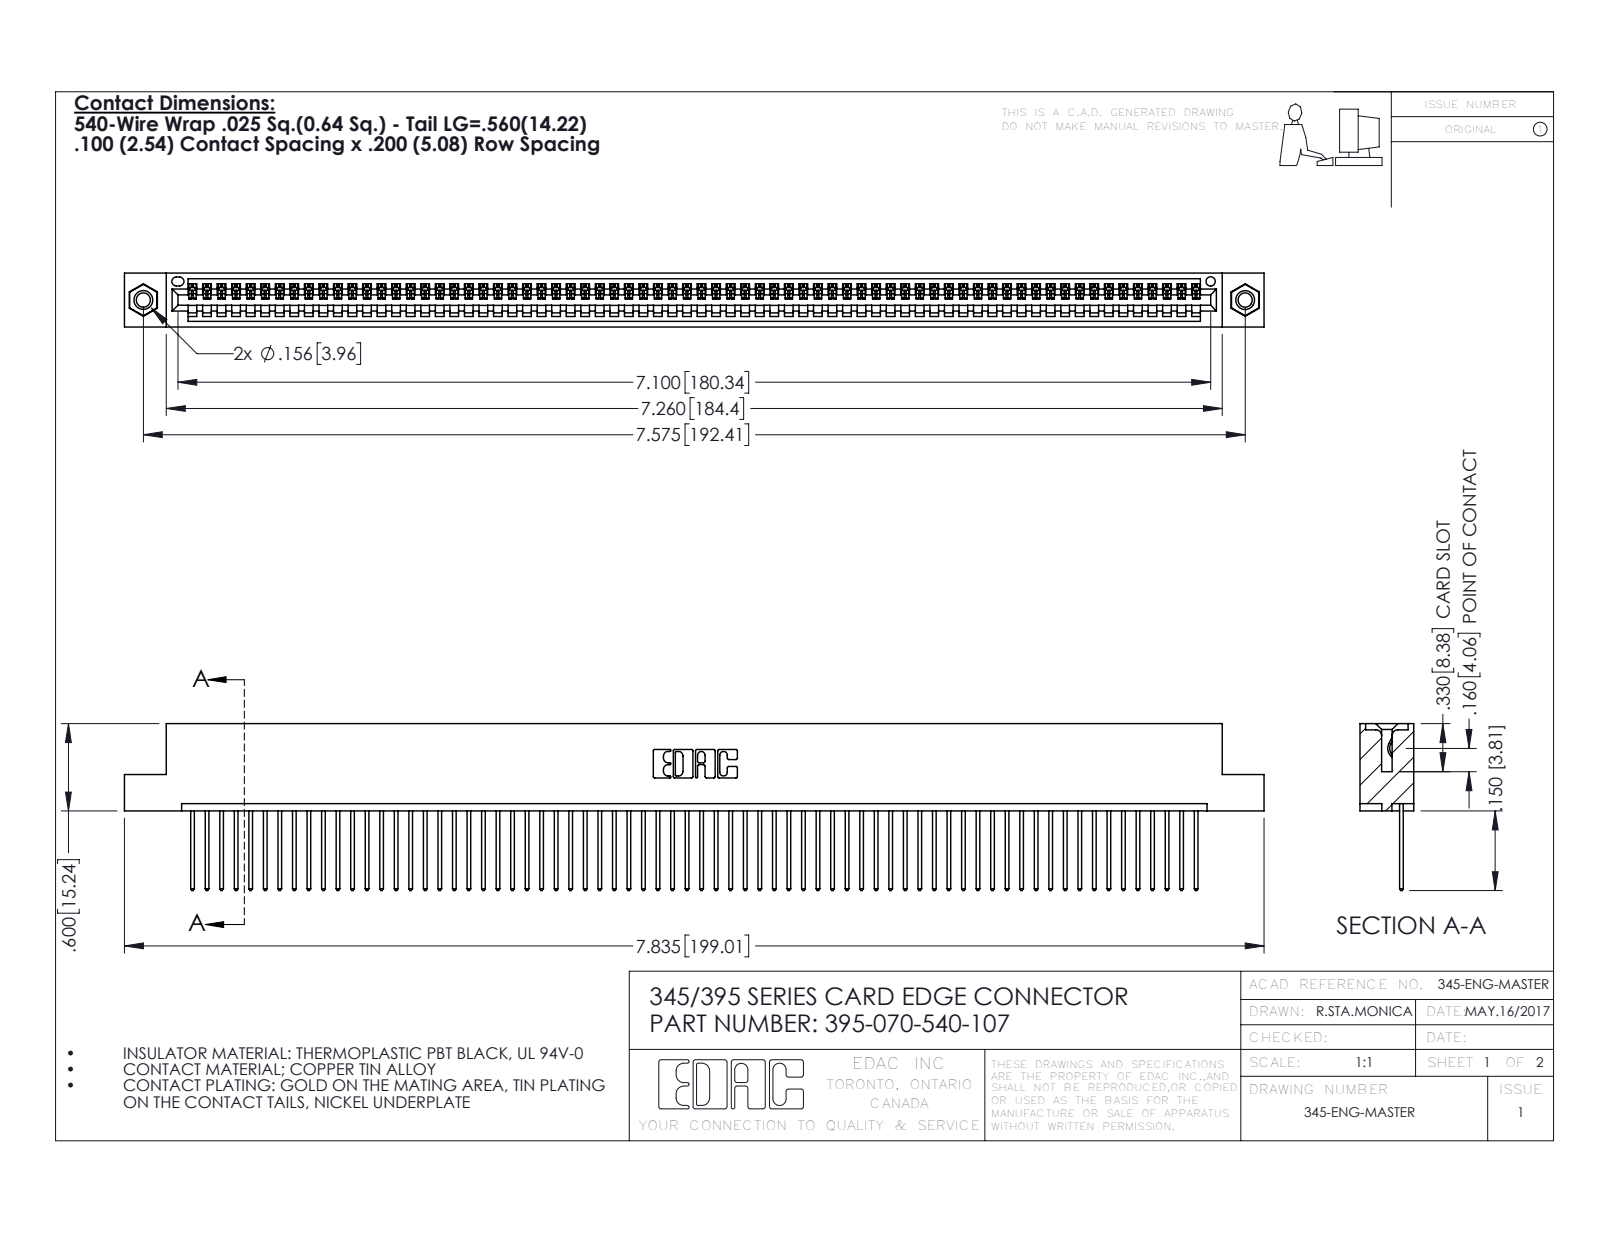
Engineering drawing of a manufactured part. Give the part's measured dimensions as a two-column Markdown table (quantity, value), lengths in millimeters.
| quantity | value |
| --- | --- |
| part name | 395-070-540-107; 345 Part_Flush Mounting Lugs - 0.156 Dia-TI; 345-292-001_345-293-140; 345-250-001_345-250-005-103 |
| STEP written by | SolidWorks 2016 (CONFIG_CONTROL_DESIGN) |
| units | millimeters |
| bodies | 73 solids, 4246 faces (2912 planar, 1318 cylindrical, 16 other) |
| overall size | 199 × 29.1 × 9.4 |
| volume | 19 210 mm³ |
| surface area | 26 630 mm² |
| round holes (diameter × count) | 2.5 × 2, 3.2 × 2, 4 × 2, 1.6 × 1 |
| round bosses / shafts (diameter × count) | 3.9 × 2 |
| partial cylindrical surfaces (radius × count) | 0.2 × 140, 0.3 × 140, 0.3 × 22, 0.2 × 6, 0.8 × 6, 0.7 × 3, 0.8 × 2, 1 × 2 |
| main face-to-face distances | 1.8, 7.6, 9.4, 2.5, 6.9, 0.6, 5.1, 5.7, 3.8, 1.8 |
| hole center spacings | 6.9, 186.4, 192.4 |
